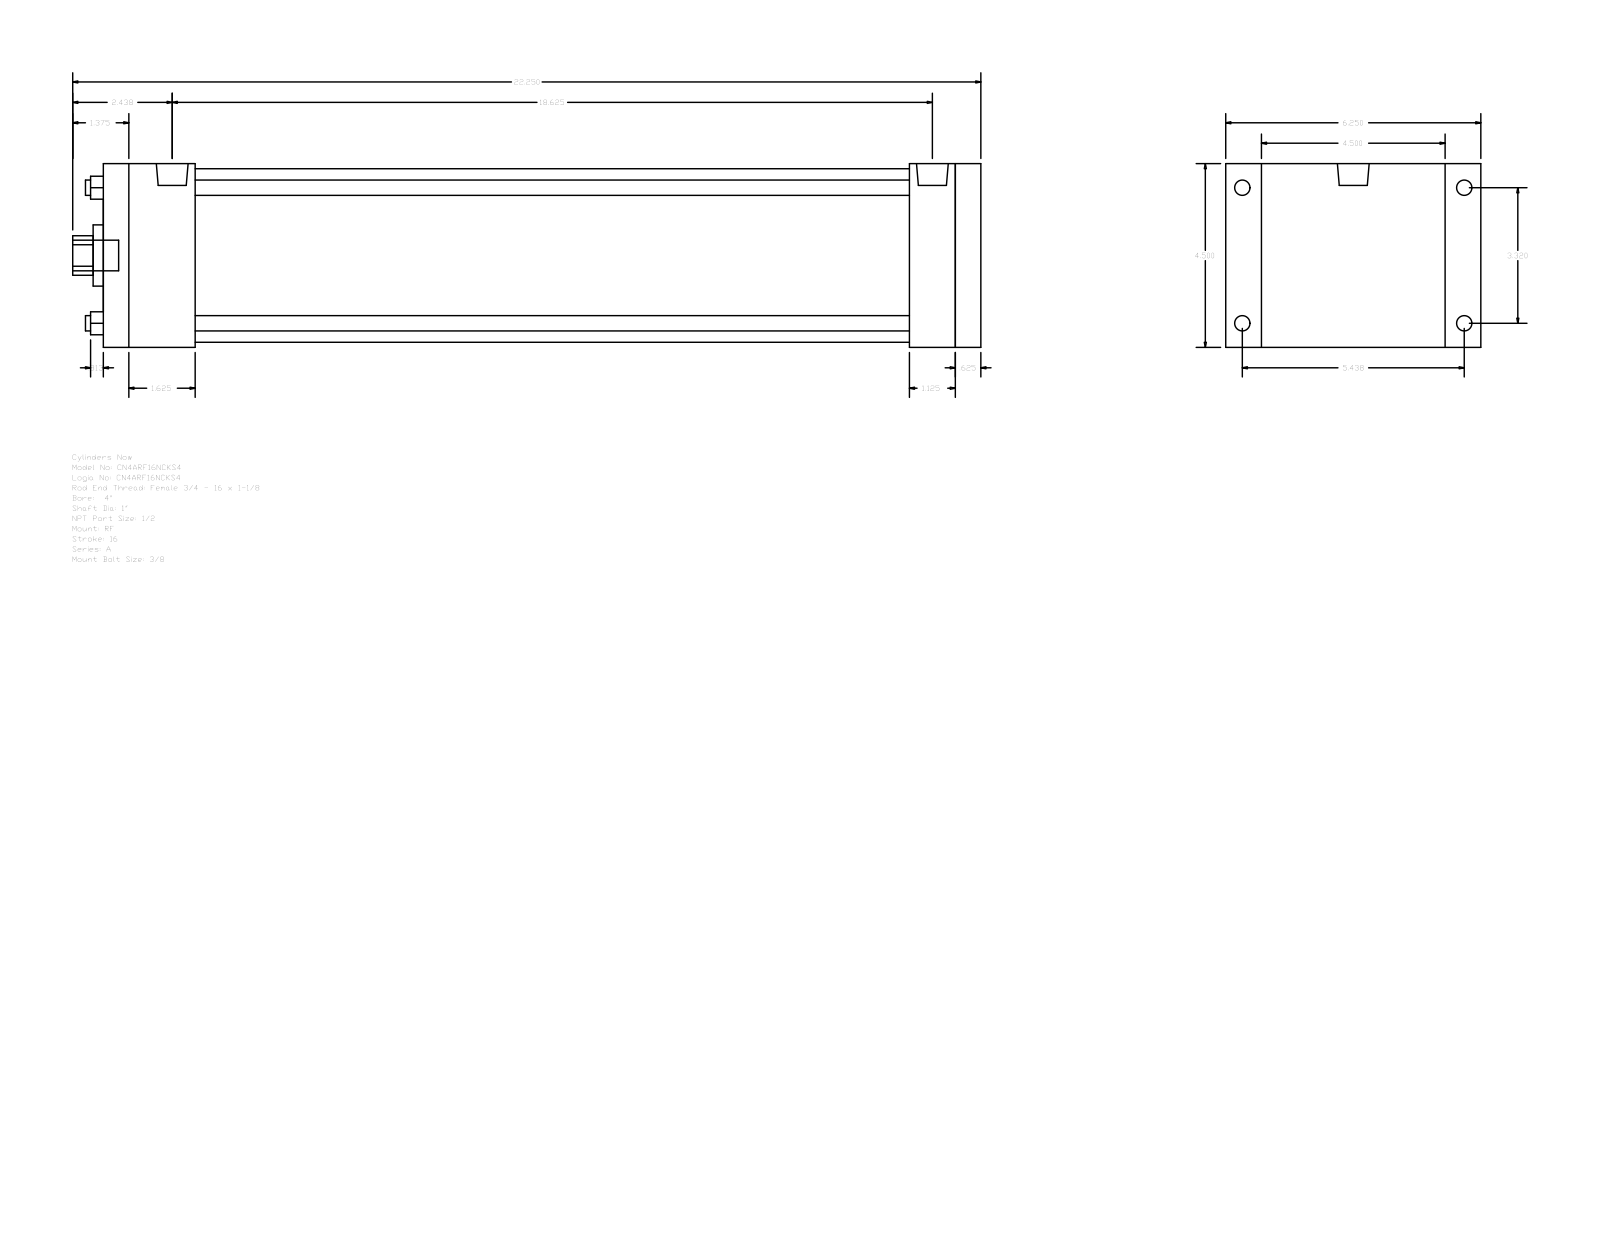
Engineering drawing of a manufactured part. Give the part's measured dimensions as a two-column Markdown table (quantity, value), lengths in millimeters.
| quantity | value |
| --- | --- |
| part name | A_RF__0400_1 |
| STEP written by | GSSL Pune (CONFIG_CONTROL_DESIGN) |
| units | millimeters |
| bodies | 0 solids, 92 faces (64 planar, 28 cylindrical, 0 other) |
| overall size | 565.15 × 158.75 × 114.3 |
| round holes (diameter × count) | 9.53 × 4, 25.4 × 1, 38.1 × 1, 107.95 × 1 |
| round bosses / shafts (diameter × count) | 9.53 × 4, 8.73 × 4, 19.77 × 2, 19.05 × 1 |
| partial cylindrical surfaces (radius × count) | 12.29 × 1 |
| main face-to-face distances | 114.3, 546.1, 530.22, 15.88, 28.57, 22.23, 136.53, 501.65, 44.45, 57.15 |
| hole center spacings | 59.62, 84.32, 119.25 |
